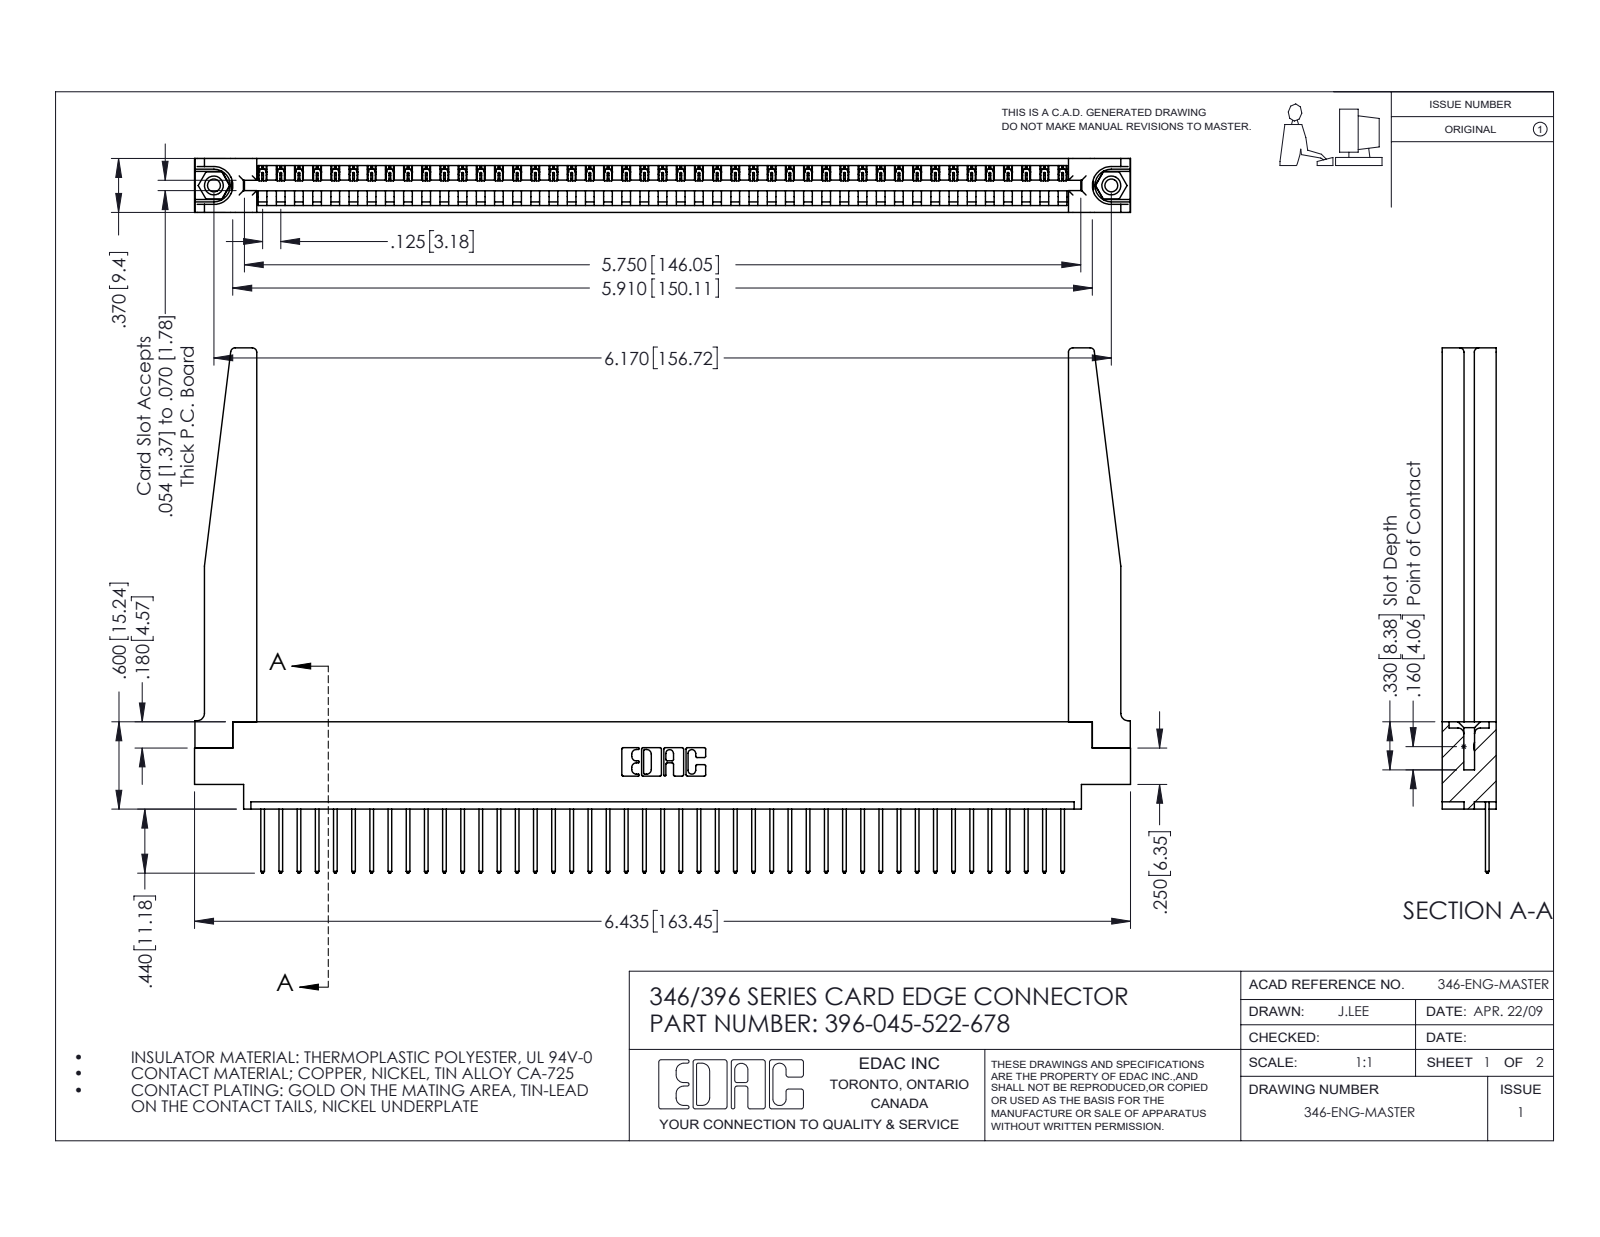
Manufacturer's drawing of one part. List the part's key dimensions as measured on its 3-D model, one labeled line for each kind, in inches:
Part name (STEP PRODUCT): 396-045-522-678; 345-250-001_345-250-001-102; 346-220-078_345-220-078; 345-292-001_345-293-122 (+1 more)
STEP written by: SolidWorks 2016 (CONFIG_CONTROL_DESIGN)
Units: inches
Bodies: 50 solids, 2970 faces (2022 planar, 896 cylindrical, 52 other)
Overall size (bounding box): 6.435 × 3.61 × 0.37
Volume: 1.369 in³ · Surface area: 40.75 in²
Round holes (diameter × count): ⌀0.089 ×2, ⌀0.125 ×2, ⌀0.156 ×2, ⌀0.064 ×1
Round bosses / shafts (diameter × count): ⌀0.155 ×2
Partial cylindrical surfaces — rounded edges, fillets, slot ends (radius × count): R0.006 ×90, R0.01 ×90, R0.01 ×22, R0.03 ×8, R0.007 ×6, R0.031 ×6, R0.026 ×3, R0.031 ×2
Main face-to-face distances: 0.37, 0.048, 0.322, 0.072, 0.148, 0.25, 0.15, 0.298, 0.025, 0.222
Hole centre spacings: 0.246, 5.961, 6.17
